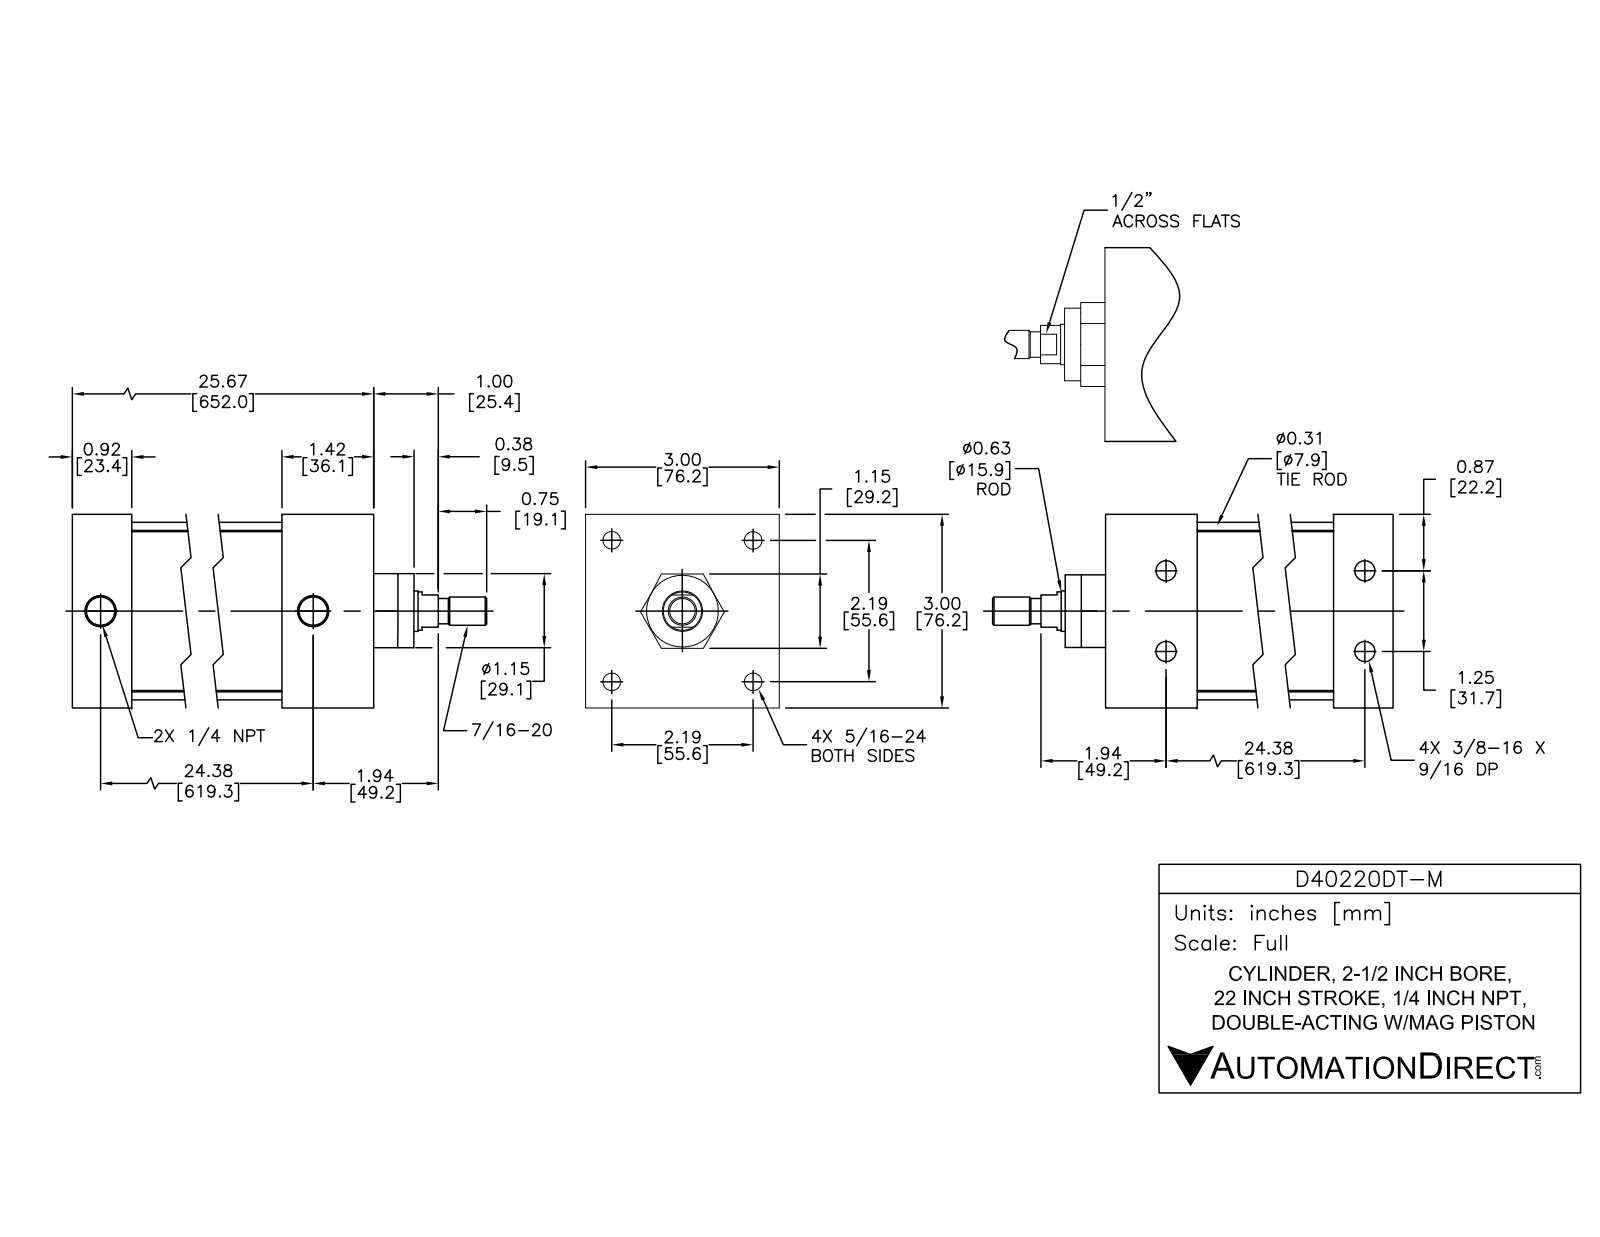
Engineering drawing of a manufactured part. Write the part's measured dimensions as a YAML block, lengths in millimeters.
part_name: "D40220DT-M; D40220DT-M PISTON; D40220DT-M BODY"
step_written_by: "SolidWorks 2015 (AUTOMOTIVE_DESIGN)"
units: millimeters
bodies: {solids: 12, faces: 298, planar: 94, cylindrical: 114, other: 90}
overall_size: [698.4, 76.2, 76.2]
volume: 1050000
surface_area: 410600
round_holes:
  - {diameter: 6.8, count: 4}
  - {diameter: 7.8, count: 4}
  - {diameter: 9.1, count: 4}
  - {diameter: 12.7, count: 4}
  - {diameter: 7.5, count: 2}
  - {diameter: 12.1, count: 2}
  - {diameter: 15.9, count: 1}
  - {diameter: 16, count: 1}
  - {diameter: 63.5, count: 1}
round_bosses_or_shafts:
  - {diameter: 12.3, count: 4}
  - {diameter: 8, count: 4}
  - {diameter: 7.2, count: 4}
  - {diameter: 69.9, count: 1}
  - {diameter: 63.4, count: 1}
  - {diameter: 28.4, count: 1}
  - {diameter: 15.8, count: 1}
  - {diameter: 15, count: 1}
partial_cylinders:
  - {radius: 7.6, count: 4}
face_to_face_distances: [76.2, 2, 592.5, 653.9, 628, 25.9, 36.1, 592, 617.9, 25.4]
hole_center_spacings: [39.5, 55.9, 619.2, 619, 15.9, 15.9, 31.8, 79]
